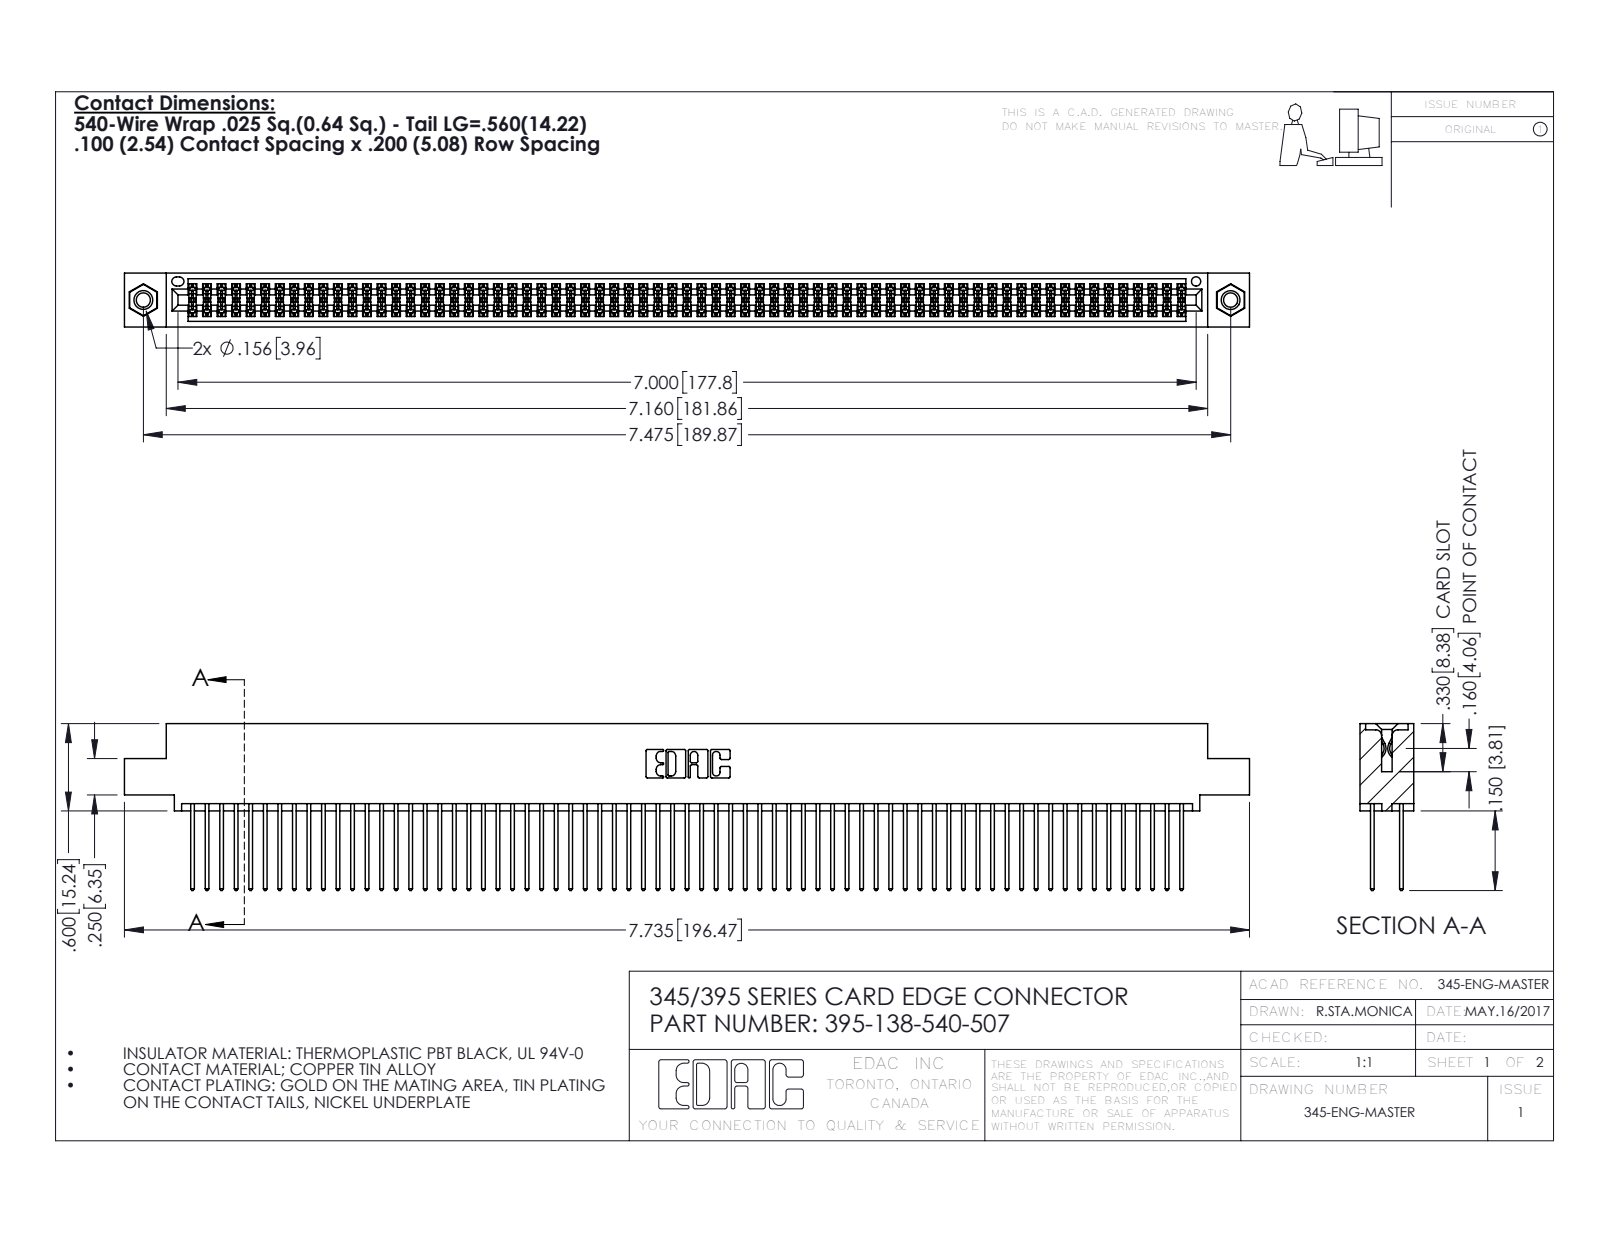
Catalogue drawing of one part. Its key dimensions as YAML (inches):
part_name: "395-138-540-507; 345-292-001_345-293-140; 345 Part_0.110 Offset - 0.156 Dia-TI; 345-250-001_345-250-005-103"
step_written_by: "SolidWorks 2016 (CONFIG_CONTROL_DESIGN)"
units: inches
bodies: {solids: 141, faces: 7090, planar: 4670, cylindrical: 2404, other: 16}
overall_size: [7.735, 1.147, 0.37]
volume: 1.207
surface_area: 50.06
round_holes:
  - {diameter: 0.098, count: 2}
  - {diameter: 0.125, count: 2}
  - {diameter: 0.156, count: 2}
  - {diameter: 0.064, count: 1}
round_bosses_or_shafts:
  - {diameter: 0.155, count: 2}
partial_cylinders:
  - {radius: 0.006, count: 207}
  - {radius: 0.01, count: 138}
  - {radius: 0.01, count: 22}
  - {radius: 0.007, count: 6}
  - {radius: 0.031, count: 6}
  - {radius: 0.026, count: 3}
  - {radius: 0.014, count: 2}
  - {radius: 0.019, count: 2}
face_to_face_distances: [0.072, 0.298, 0.2, 0.098, 0.272, 0.025, 0.225, 0.37, 0.175, 0.149]
hole_center_spacings: [0.27, 7.239, 7.475]
